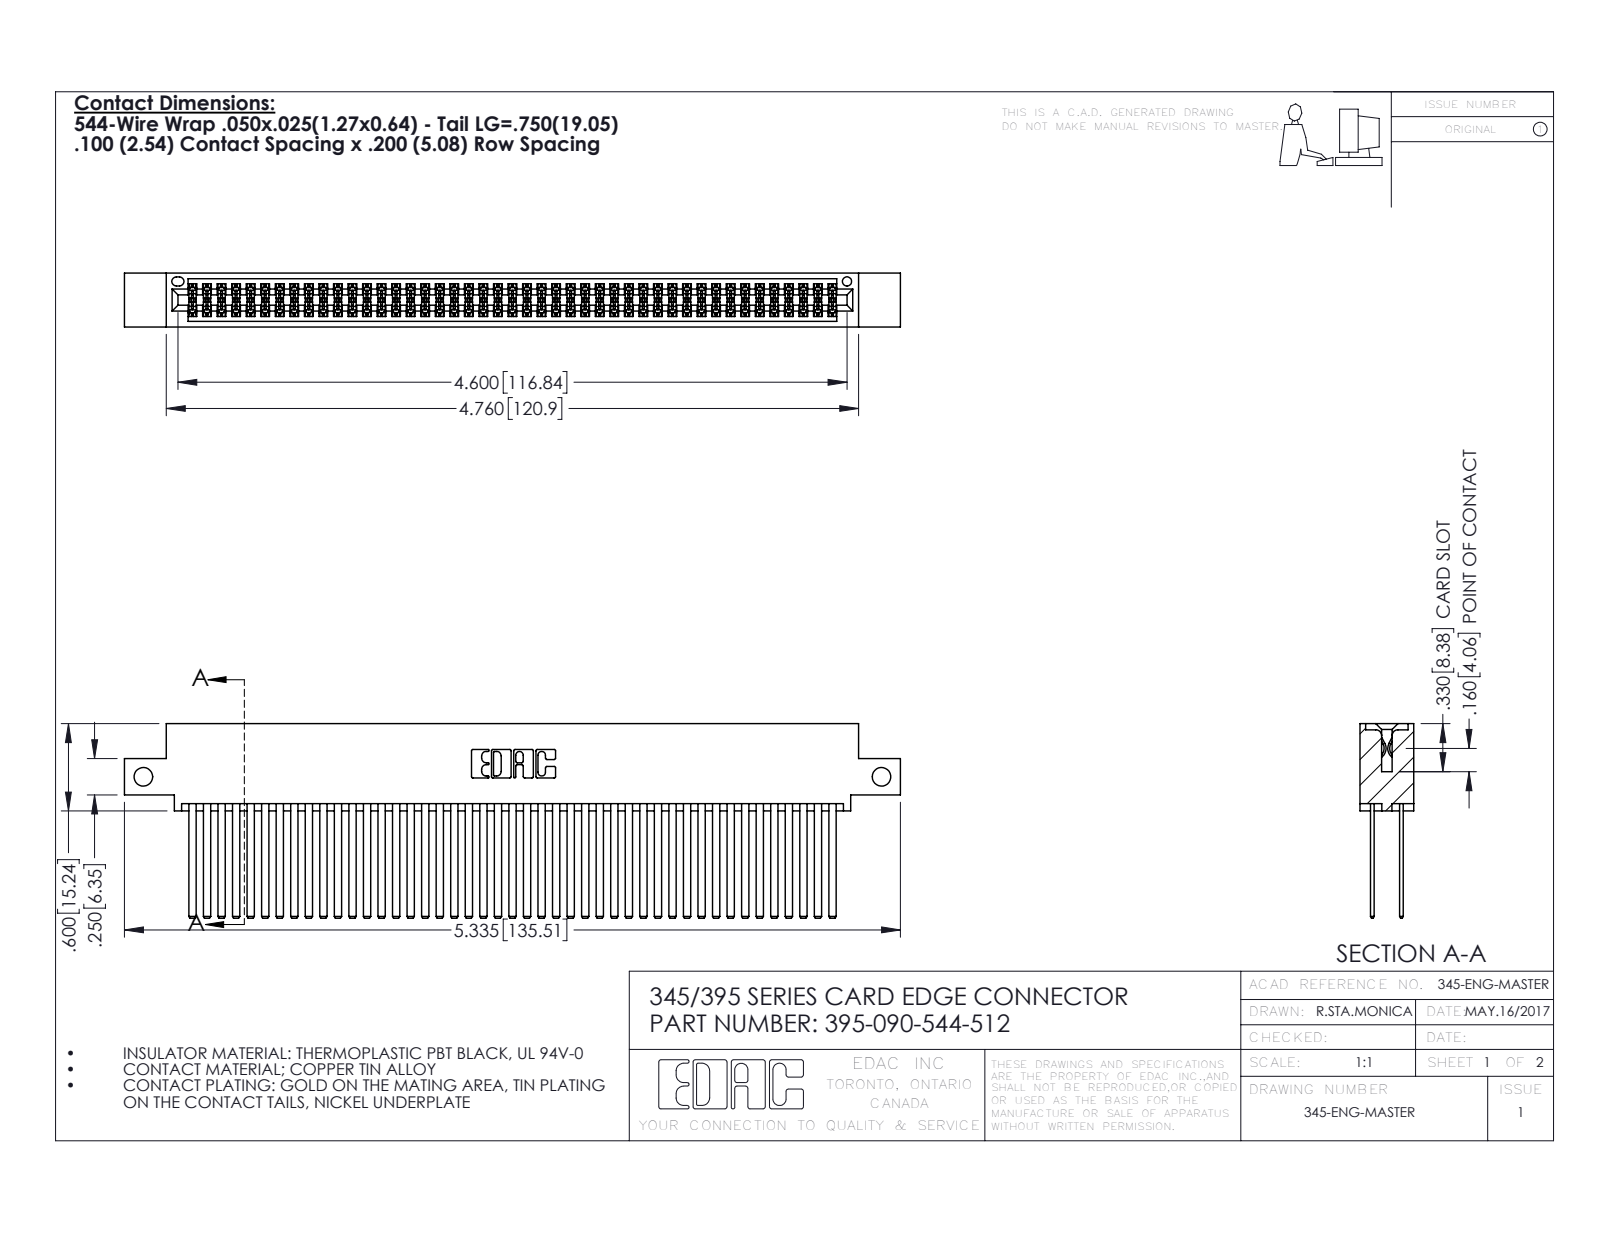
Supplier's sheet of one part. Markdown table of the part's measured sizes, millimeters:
| quantity | value |
| --- | --- |
| part name | 345 Part_0.110 Offset - Side Mount; 345-292-001_345-293-144; 395-090-544-512 |
| STEP written by | SolidWorks 2016 (CONFIG_CONTROL_DESIGN) |
| units | millimeters |
| bodies | 91 solids, 4090 faces (2694 planar, 1396 cylindrical, 0 other) |
| overall size | 135.5 × 34 × 9.4 |
| volume | 14 300 mm³ |
| surface area | 24 840 mm² |
| round holes (diameter × count) | 3.3 × 2, 1.6 × 1 |
| partial cylindrical surfaces (radius × count) | 0.2 × 135, 0.3 × 22, 0.2 × 6, 0.8 × 6, 0.7 × 3, 0.4 × 2, 0.5 × 2, 0.6 × 2 |
| main face-to-face distances | 5.1, 0.6, 7.6, 1.8, 2.5, 6.9, 5.7, 4.4, 9.4, 1.3 |
| hole center spacings | 128.9 |
